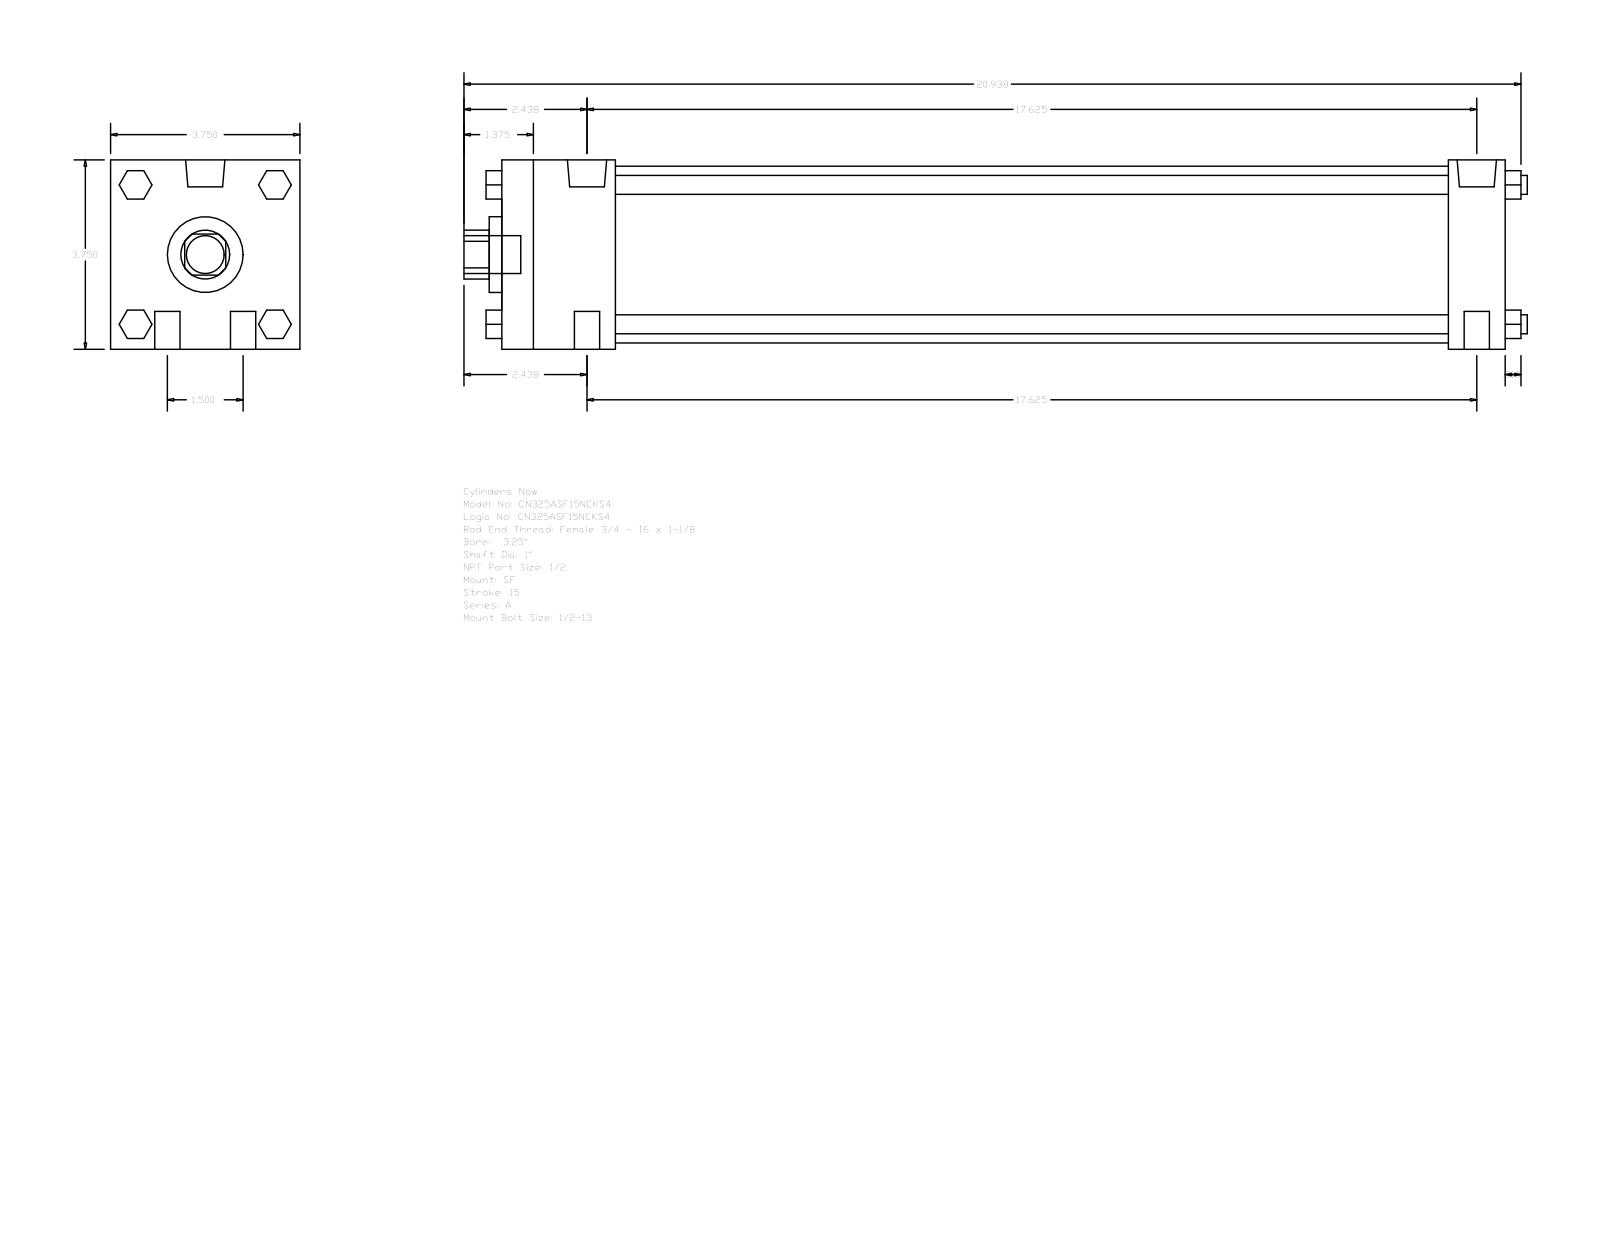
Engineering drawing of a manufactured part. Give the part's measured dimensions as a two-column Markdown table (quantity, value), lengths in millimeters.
| quantity | value |
| --- | --- |
| part name | A_SF__0325_1 |
| STEP written by | GSSL Pune (CONFIG_CONTROL_DESIGN) |
| units | millimeters |
| bodies | 0 solids, 124 faces (94 planar, 30 cylindrical, 0 other) |
| overall size | 534.99 × 95.25 × 95.25 |
| round holes (diameter × count) | 25.4 × 1, 38.1 × 1, 88.9 × 1 |
| round bosses / shafts (diameter × count) | 12.7 × 4, 9.53 × 4, 19.77 × 2, 8.73 × 2, 19.05 × 1 |
| partial cylindrical surfaces (radius × count) | 12.29 × 1 |
| main face-to-face distances | 95.24, 504.83, 476.25, 28.58, 57.15, 419.1, 447.68, 14.28, 35.05, 60.71 |
